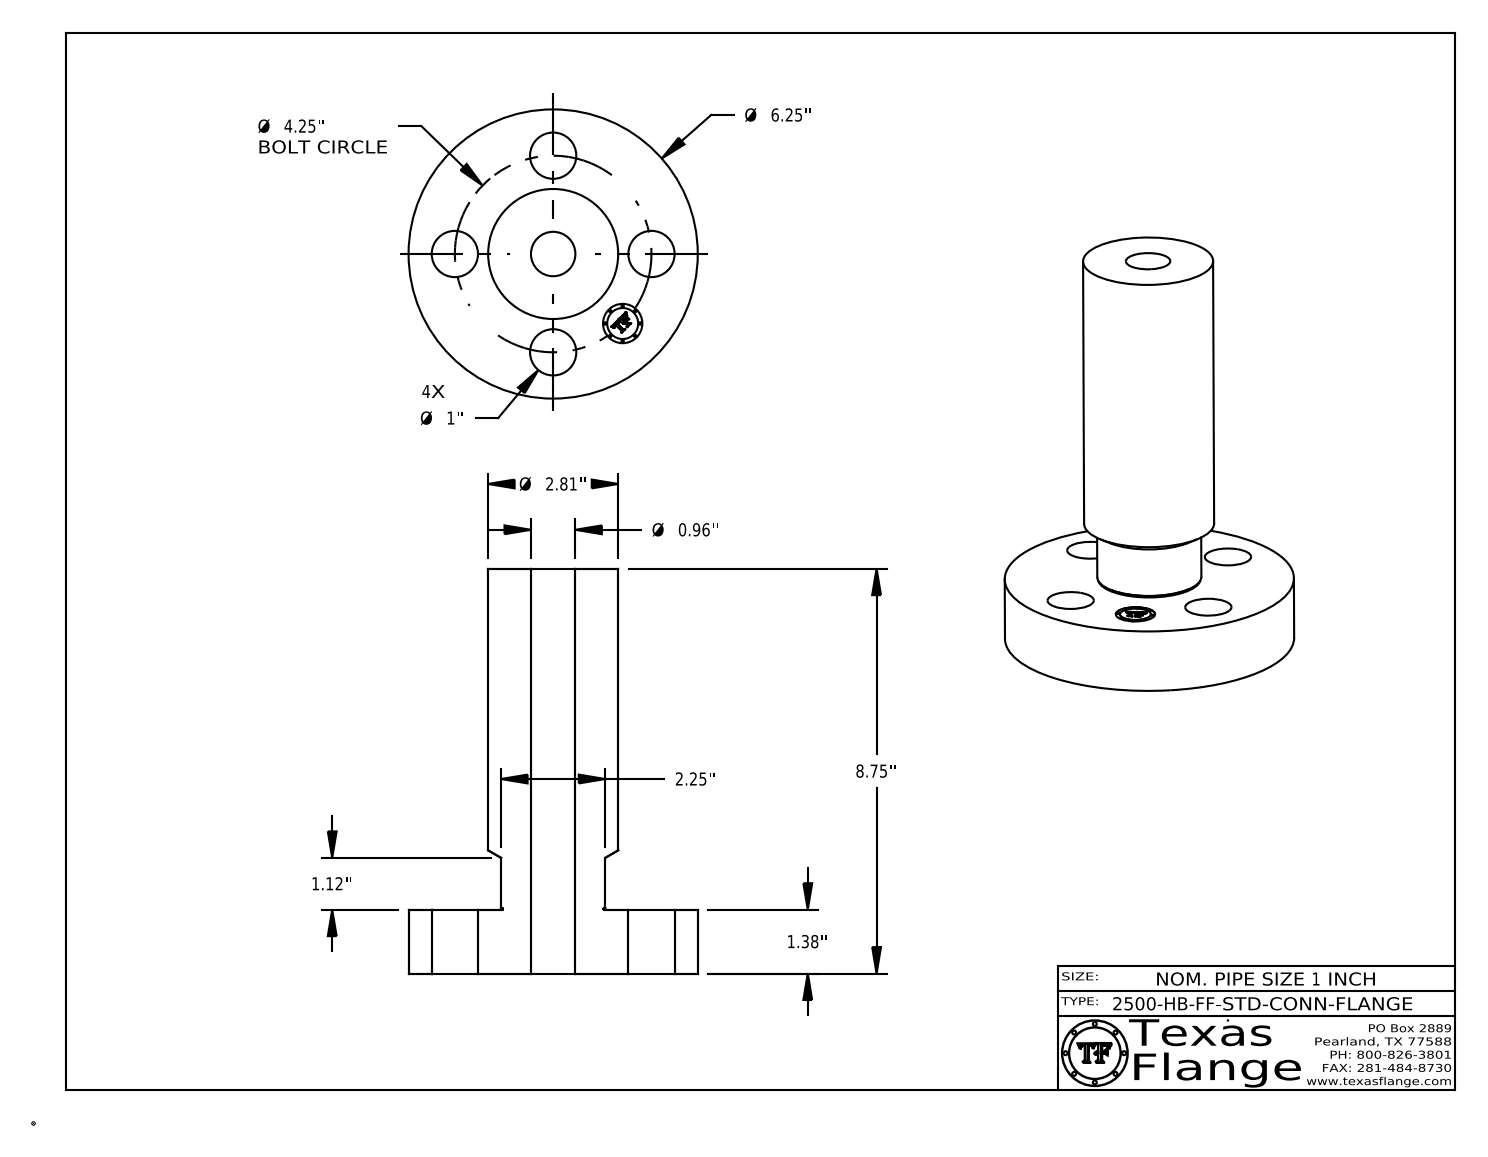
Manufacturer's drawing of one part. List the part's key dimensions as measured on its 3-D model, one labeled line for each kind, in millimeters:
Part name (STEP PRODUCT): 1-2500-HB-FF-STD-CONN-FLANGE
STEP written by: CATIA V5 STEP AP214 (AUTOMOTIVE_DESIGN)
Units: millimetres
Bodies: 1 solid, 410 faces (368 planar, 36 cylindrical, 6 other)
Overall size (bounding box): 222.3 × 158.8 × 158.8
Volume: 1 224 000 mm³ · Surface area: 123 400 mm²
Round holes (diameter × count): ⌀25.4 ×4, ⌀21.6 ×1, ⌀24.4 ×1
Round bosses / shafts (diameter × count): ⌀1.3 ×8, ⌀158.8 ×1, ⌀71.4 ×1, ⌀57.2 ×1, ⌀17 ×1
Main face-to-face distances: 35.1, 222.3, 187.2, 34.9, 187.3, 6.5, 6.3, 0.4, 1.2, 4.2
Hole centre spacings: 54, 76.4, 41.3, 99.7, 108
